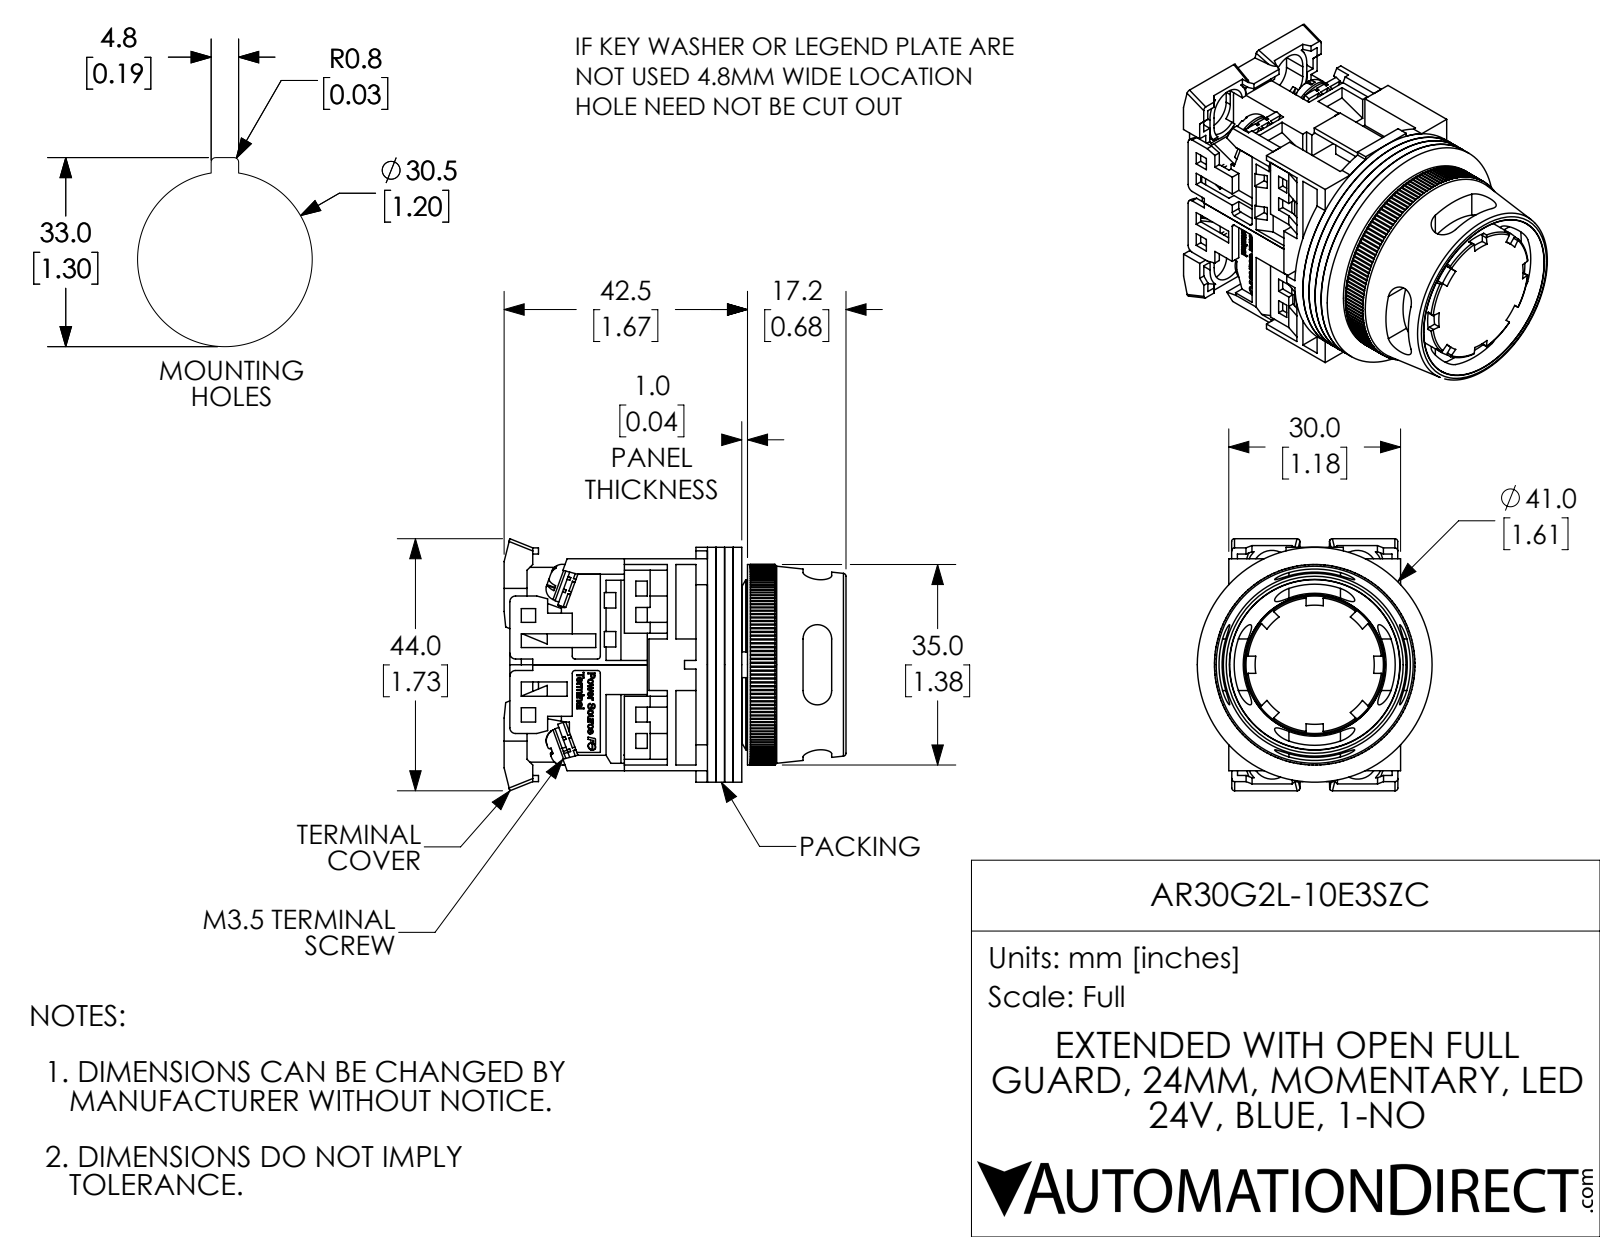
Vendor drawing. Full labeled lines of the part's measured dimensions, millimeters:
Part name (STEP PRODUCT): AR30G2L-10E3SZC
STEP written by: SolidWorks 2017 (AUTOMOTIVE_DESIGN)
Units: millimetres
Bodies: 25 solids, 2179 faces (1508 planar, 458 cylindrical, 213 other)
Overall size (bounding box): 59.7 × 44 × 41
Volume: 35 100 mm³ · Surface area: 40 400 mm²
Round holes (diameter × count): ⌀3.5 ×8, ⌀3.6 ×4, ⌀3 ×1, ⌀12 ×1, ⌀18 ×1, ⌀18.5 ×1, ⌀20 ×1, ⌀24 ×1, ⌀31.8 ×1
Round bosses / shafts (diameter × count): ⌀6.6 ×4, ⌀3.5 ×4, ⌀41 ×1, ⌀35 ×1, ⌀30 ×1, ⌀22 ×1, ⌀19.7 ×1, ⌀14 ×1
Partial cylindrical surfaces — rounded edges, fillets, slot ends (radius × count): R0.3 ×160, R0.3 ×16, R1.5 ×16, R0.5 ×12, R1 ×4, R2.5 ×4, R3.5 ×4, R4.5 ×4
Main face-to-face distances: 1.5, 3, 1, 4.5, 7, 36, 18.5, 20.6, 2, 34.5
Hole centre spacings: 14.7, 15.5
